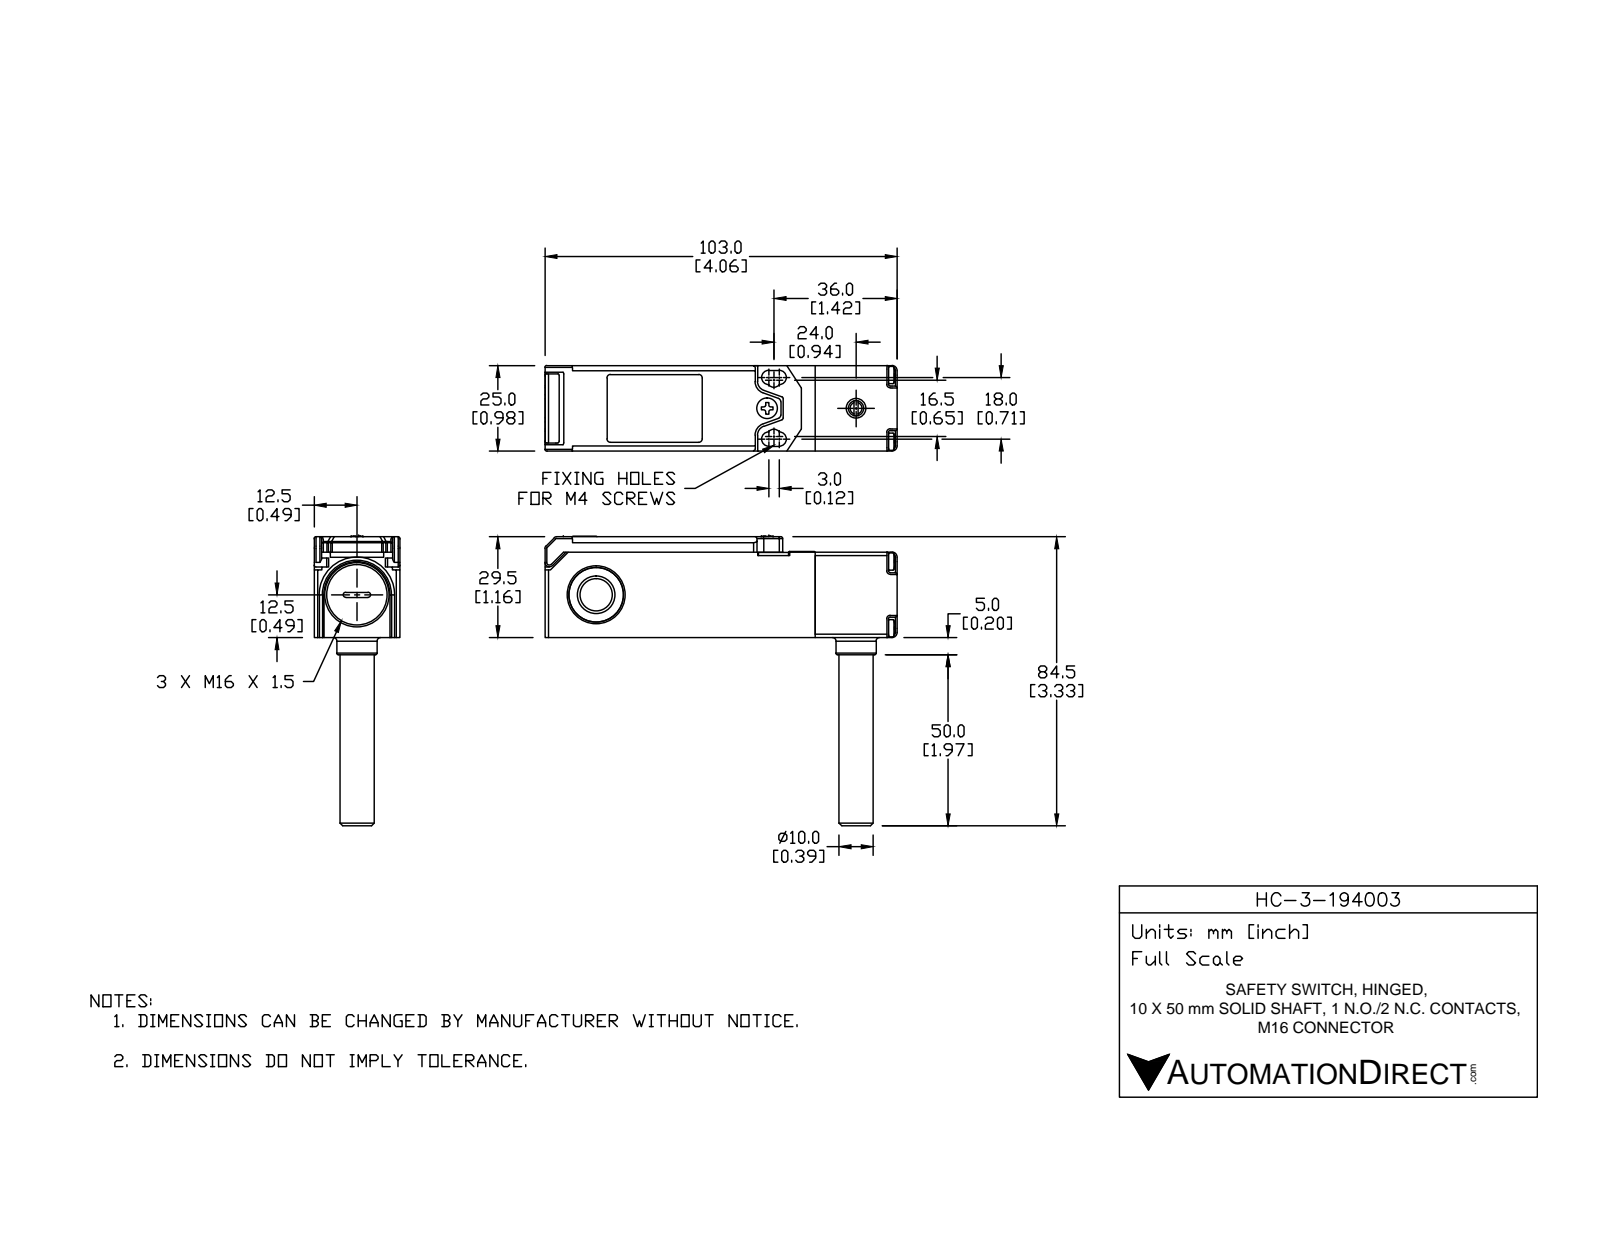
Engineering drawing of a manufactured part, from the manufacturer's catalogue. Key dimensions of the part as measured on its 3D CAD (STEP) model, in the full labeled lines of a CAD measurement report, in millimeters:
Part name (STEP PRODUCT): HC-3-194003
STEP written by: SolidWorks 2014 (AUTOMOTIVE_DESIGN)
Units: millimetres
Bodies: 13 solids, 1848 faces (866 planar, 583 cylindrical, 399 other)
Overall size (bounding box): 103 × 84.7 × 25
Volume: 34 200 mm³ · Surface area: 33 150 mm²
Round holes (diameter × count): ⌀3.2 ×5, ⌀2.4 ×4, ⌀1.5 ×2, ⌀1.6 ×2, ⌀1.8 ×2, ⌀2.2 ×2, ⌀3.6 ×2, ⌀16 ×2, ⌀1.4 ×1, ⌀2.1 ×1, ⌀2.5 ×1, ⌀2.6 ×1
Round bosses / shafts (diameter × count): ⌀2.6 ×5, ⌀5 ×4, ⌀2 ×4, ⌀3.5 ×2, ⌀10 ×1, ⌀9.8 ×1, ⌀6.5 ×1, ⌀5.8 ×1
Partial cylindrical surfaces — rounded edges, fillets, slot ends (radius × count): R0.5 ×225, R0.1 ×24, R1 ×21, R0.3 ×12, R1.5 ×6, R2.1 ×6, R2.8 ×6, R3.5 ×6
Main face-to-face distances: 25, 2, 1.8, 23.2, 4.5, 23, 2.5, 1, 21, 2.2
Hole centre spacings: 13.8, 19.5, 4.3, 4.7, 6.2, 10.5, 10.7, 10.8
